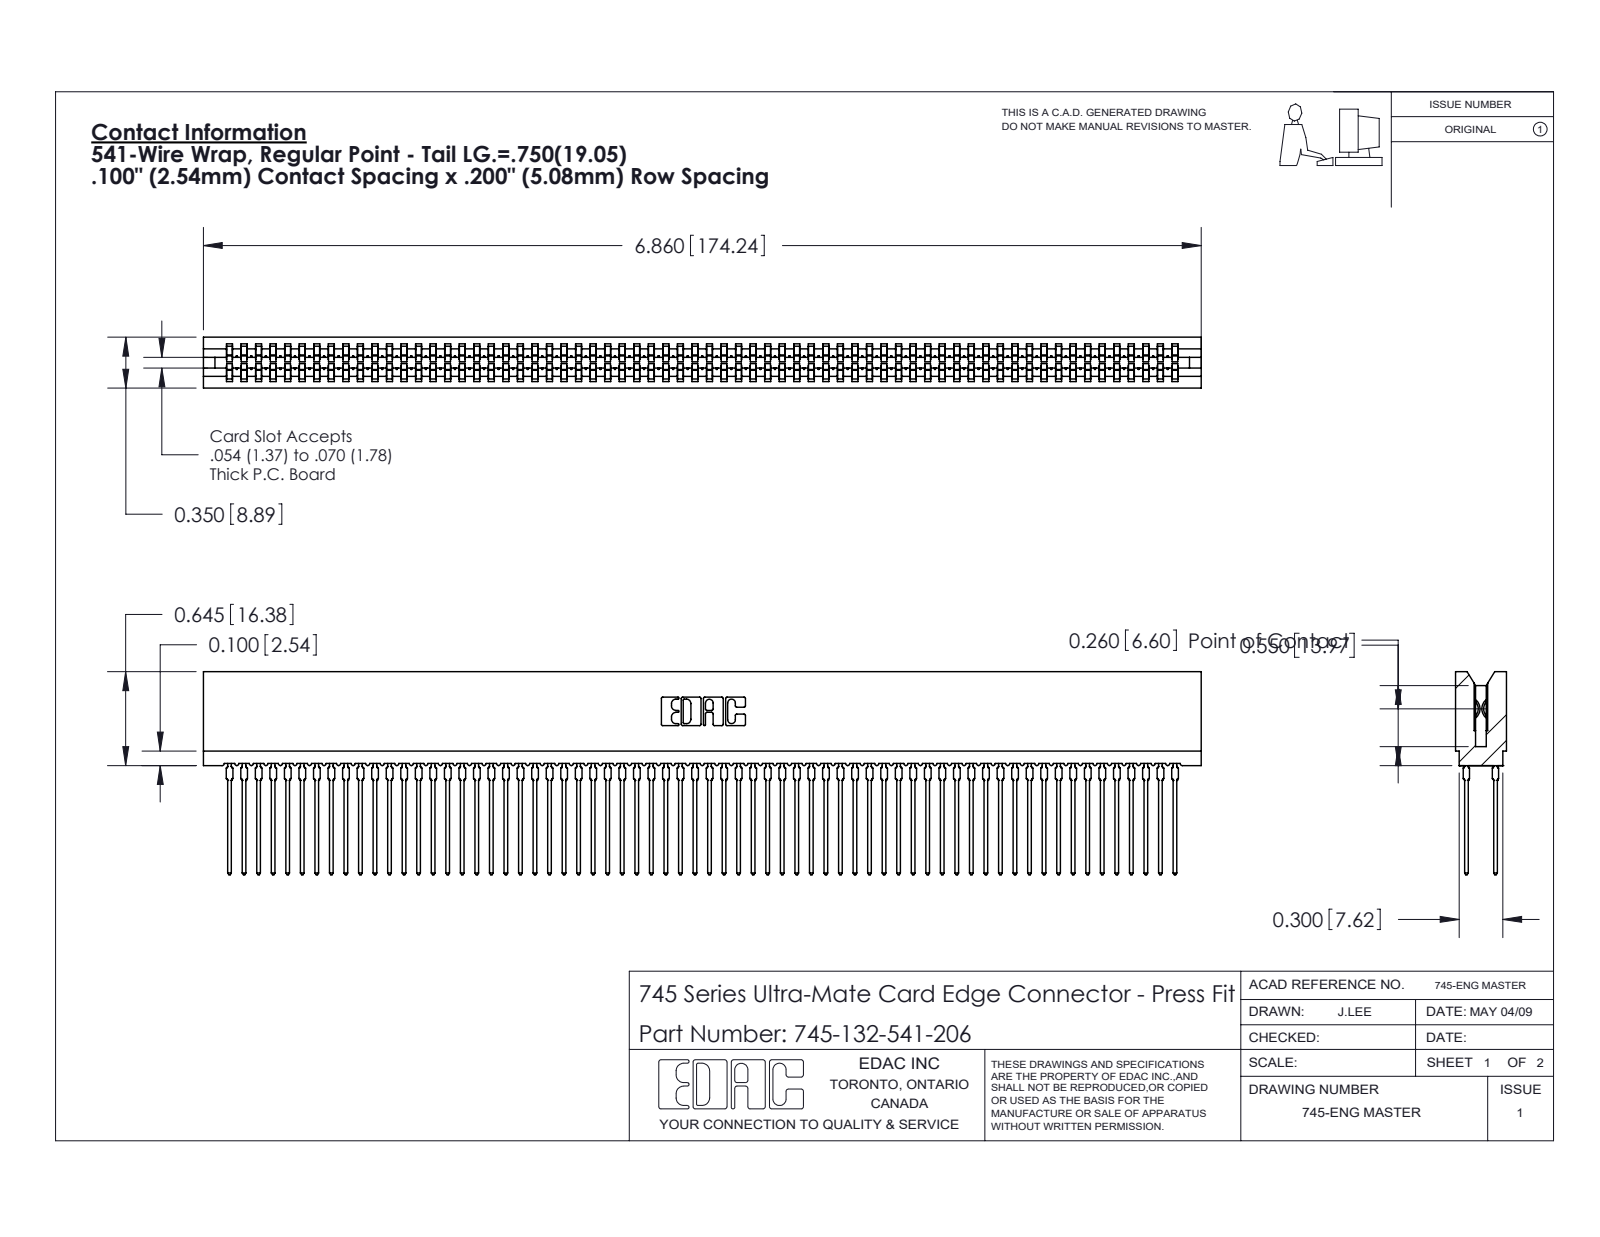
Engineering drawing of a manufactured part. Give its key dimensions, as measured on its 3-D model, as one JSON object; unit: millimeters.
{"part_name": "745 Part_Insulator Option - 06; 745-132-541-206; 745-292-001_541", "step_written_by": "SolidWorks 2020 (CONFIG_CONTROL_DESIGN)", "units": "millimeters", "bodies": {"solids": 133, "faces": 11910, "planar": 6128, "cylindrical": 2350, "other": 3432}, "overall_size": [174.2, 35.5, 8.9], "volume_mm3": 16200, "surface_area_mm2": 36080, "partial_cylinders_radius": [[0.5, 264], [0.4, 132], [0.3, 22], [0.1, 8], [0.3, 8], [0.2, 6], [0.8, 6], [0.7, 3]], "face_to_face_distances": [1.6, 7.3, 8.9, 5.1, 2.2, 6.7, 0.6, 1.1, 7.7, 0.5]}
